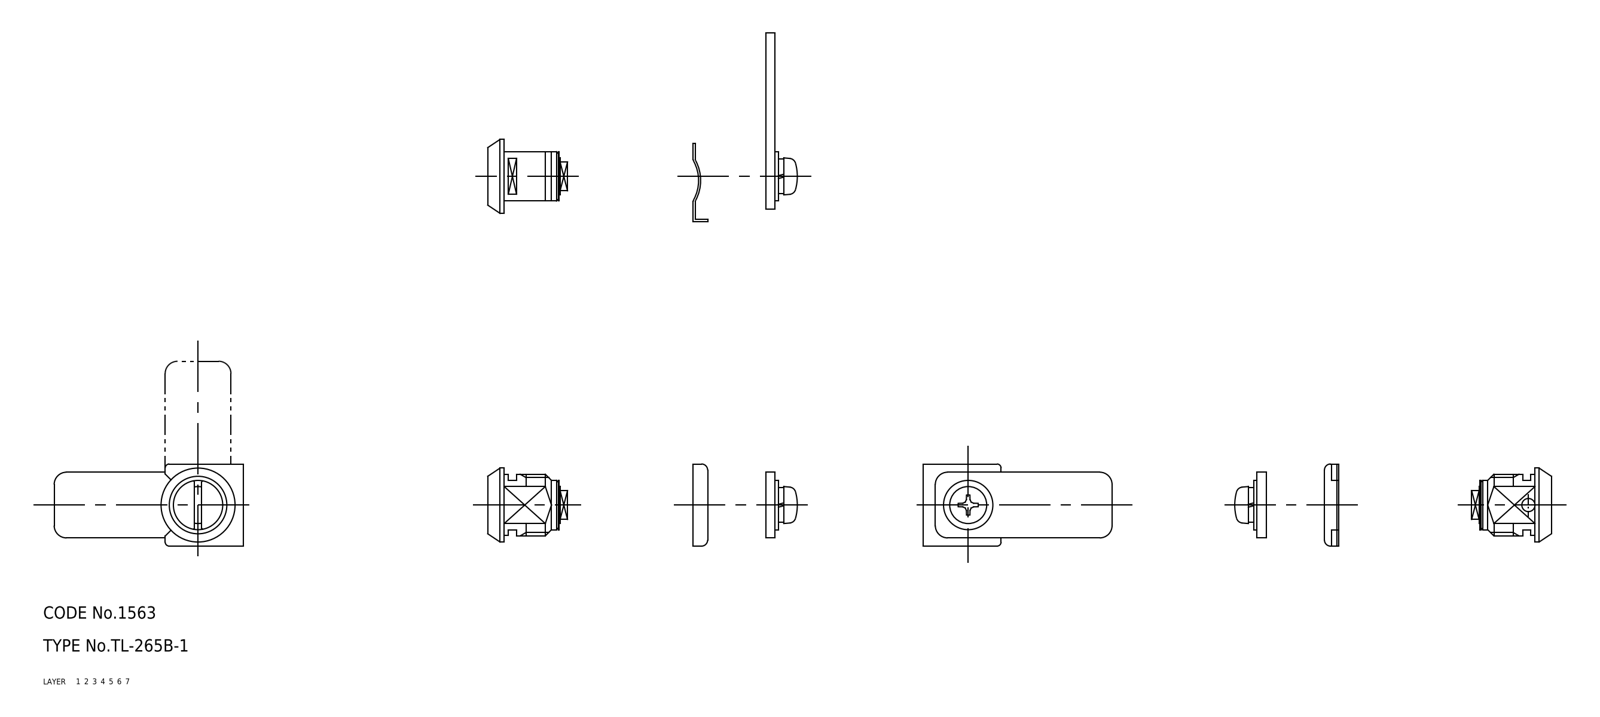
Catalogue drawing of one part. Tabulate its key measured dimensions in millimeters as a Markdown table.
| quantity | value |
| --- | --- |
| part name | retainer_2; retainer_1; shaft; screw (+2 more) |
| STEP written by | CADfix (AUTOMOTIVE_DESIGN) |
| units | millimeters |
| bodies | 6 solids, 161 faces (0 planar, 0 cylindrical, 161 other) |
| overall size | 46 × 25.27 × 20 |
| volume | 4 509 mm³ |
| surface area | 5 283 mm² |
